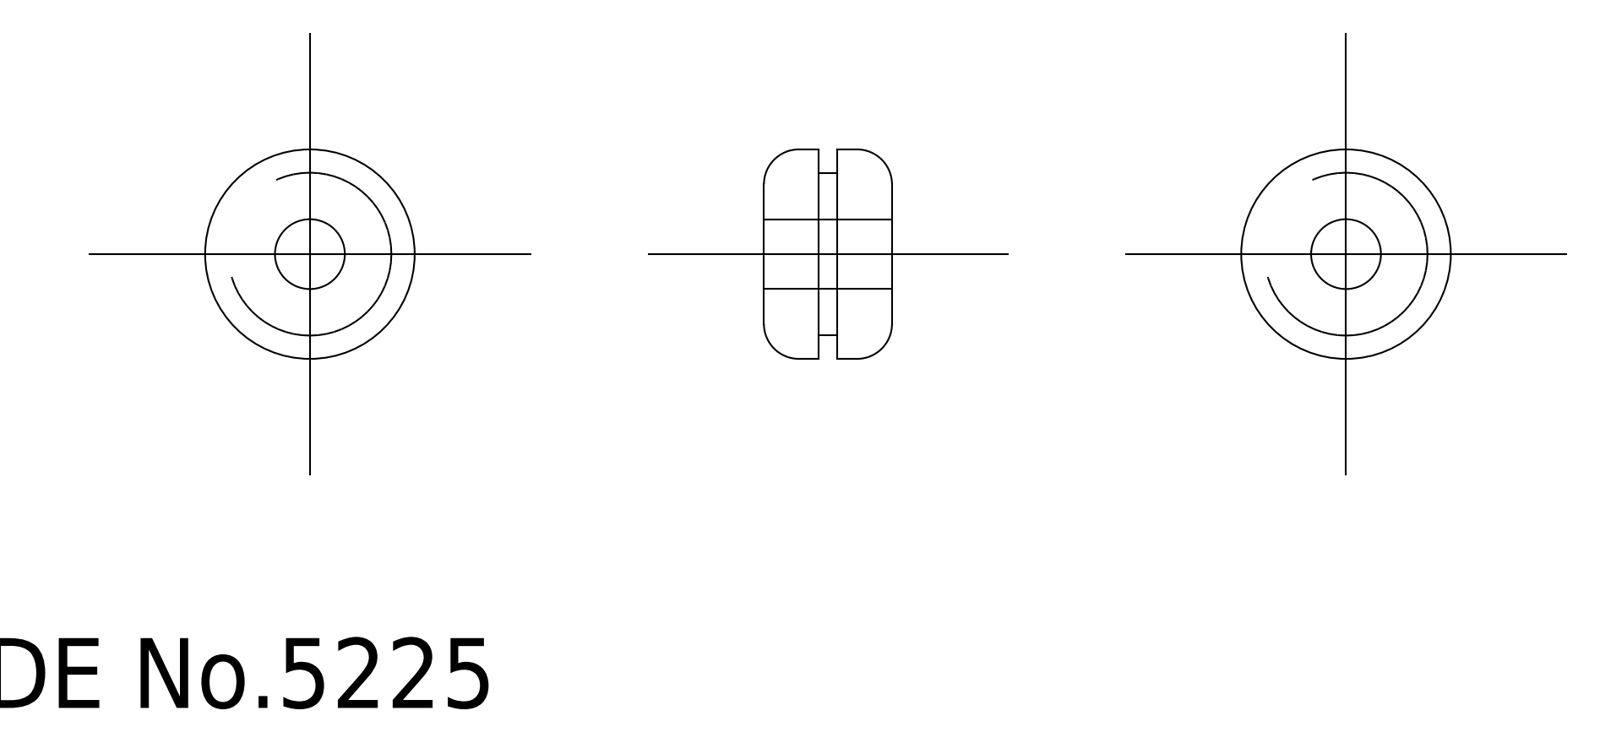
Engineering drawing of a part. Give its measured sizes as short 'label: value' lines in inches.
name: grommet
written by: CADfix (AUTOMOTIVE_DESIGN)
unit: in
bodies: 1 solid, 16 faces (0 planar, 0 cylindrical, 16 other)
size: 0.354 × 0.354 × 0.217
volume: 0.016 in³; area: 0.507 in²
